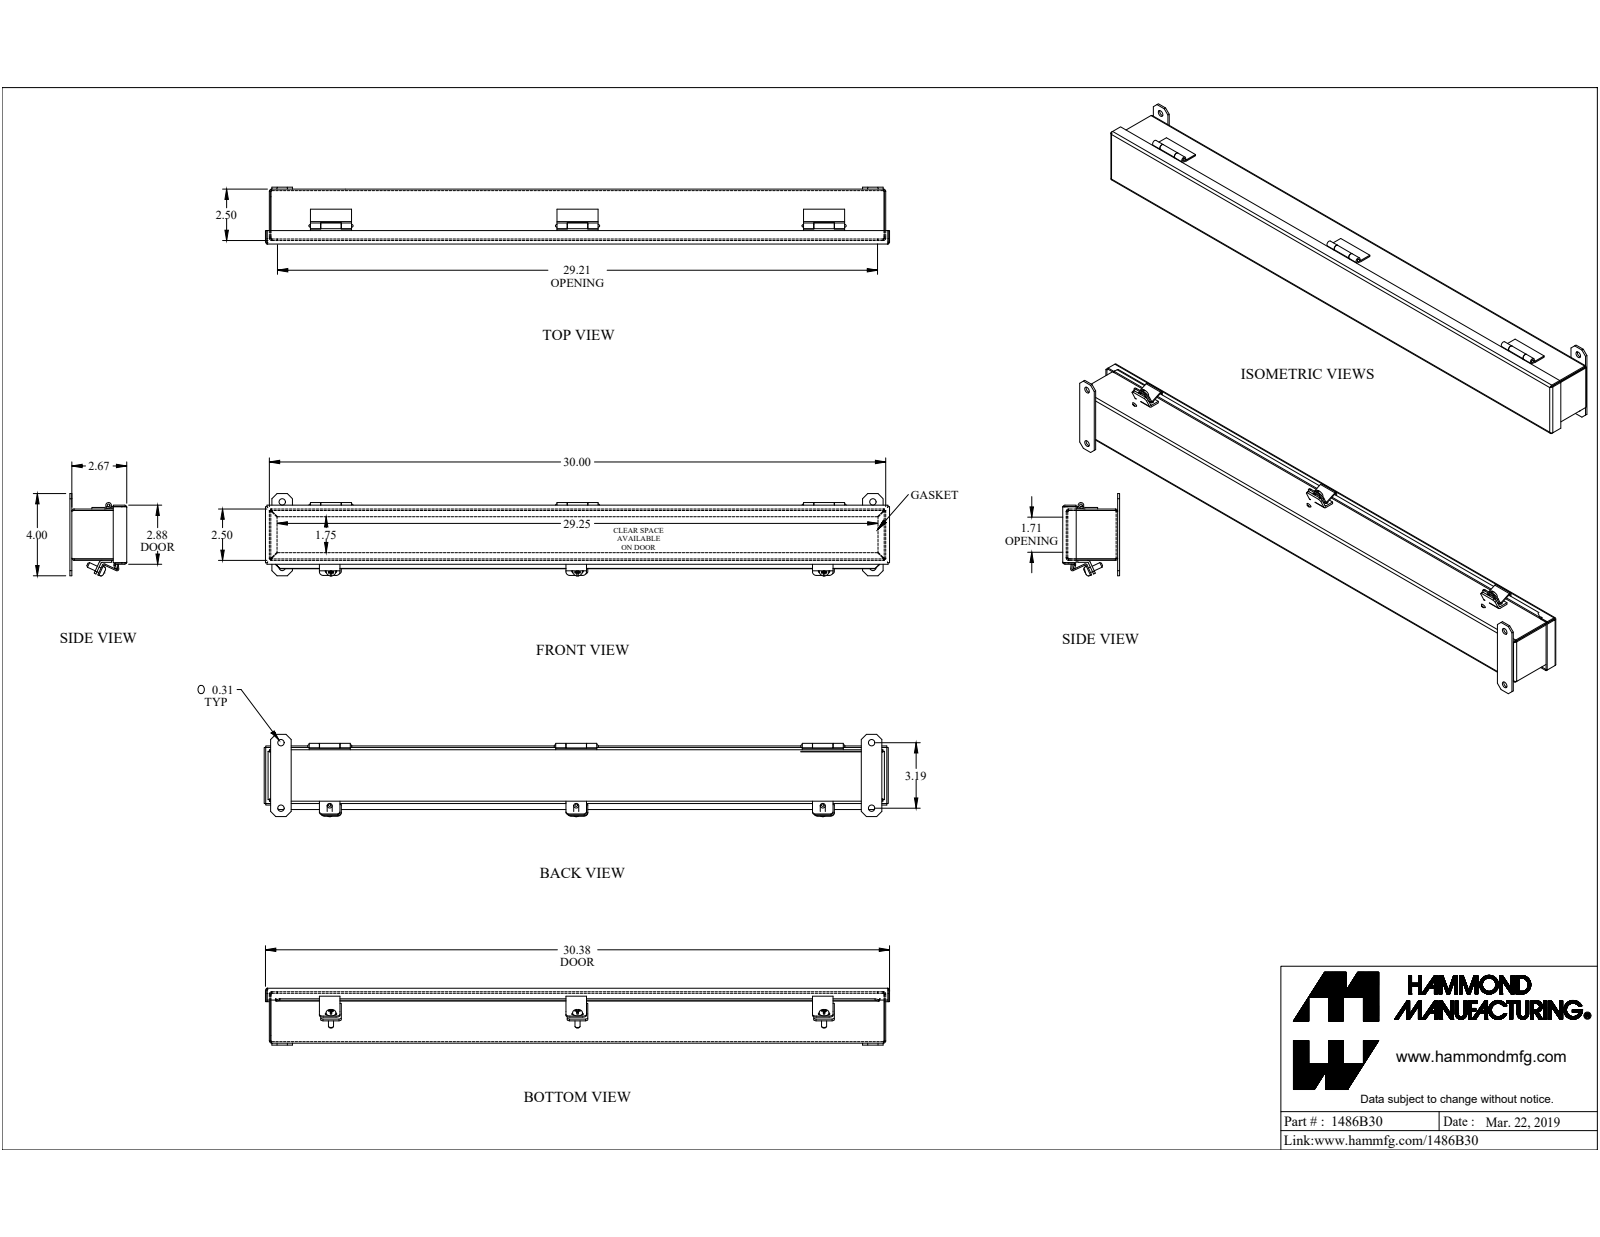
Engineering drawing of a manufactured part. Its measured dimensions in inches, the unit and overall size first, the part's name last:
Units: inches
Overall size (bounding box): 30.375 × 4.006 × 2.767
Round holes (diameter × count): ⌀0.313 ×4, ⌀0.213 ×3, ⌀0.125 ×1
Round bosses / shafts (diameter × count): ⌀0.48 ×3, ⌀0.246 ×3, ⌀0.275 ×1, ⌀0.125 ×1
Partial cylindrical surfaces — rounded edges, fillets, slot ends (radius × count): R0.036 ×13, R0.108 ×13, R0.188 ×12, R0.25 ×12, R0.01 ×6, R0.141 ×6, R0.029 ×2, R0.086 ×2
Main face-to-face distances: 0.072, 2.428, 2.6, 2.5, 2.356, 2.672, 2.528, 2.615, 0.187, 0.187
Hole centre spacings: 3.188, 12, 28.75, 28.926, 24
Volume: 35.4 in³ · Surface area: 917.6 in²
Bodies: 26 solids, 536 faces (355 planar, 124 cylindrical, 57 other)
Part name (STEP PRODUCT): 1486B30
STEP written by: SolidWorks 2019 (CONFIG_CONTROL_DESIGN)
